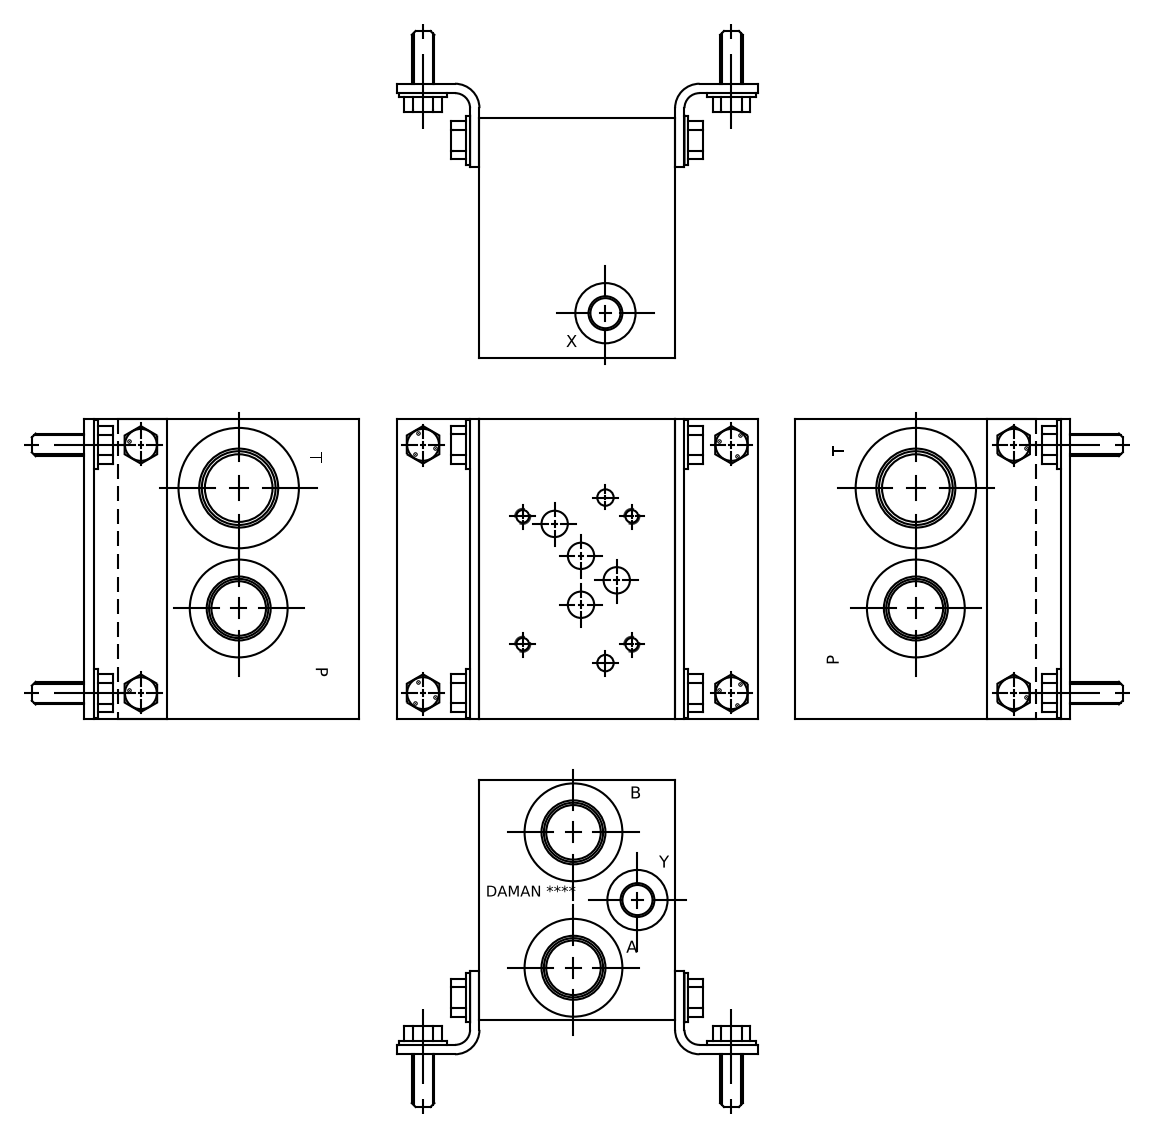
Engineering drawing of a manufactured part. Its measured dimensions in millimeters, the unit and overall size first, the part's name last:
Units: millimetres
Overall size (bounding box): 127 × 101.6 × 82.55
Round holes (diameter × count): ⌀6.35 ×5, ⌀5.11 ×4, ⌀11.11 ×3, ⌀23.01 ×3, ⌀24.92 ×3, ⌀27.43 ×3, ⌀42.04 ×3, ⌀7.92 ×2, ⌀9.53 ×2, ⌀12.7 ×2, ⌀14.27 ×2, ⌀14.53 ×2
Main face-to-face distances: 101.6, 82.55, 0.79, 127, 81.76, 126.21, 80.97, 19.05, 19.84, 62.71
Hole centre spacings: 18.28, 26.69, 35.83, 46.41, 13.64, 13.65, 13.86, 13.87
Volume: 916 382 mm³ · Surface area: 87 627 mm²
Bodies: 1 solid, 593 faces (344 planar, 63 cylindrical, 186 other)
Part name (STEP PRODUCT): Part_DD05HP013S~24_3D
STEP written by: Autodesk Inventor 2019 (AUTOMOTIVE_DESIGN)
